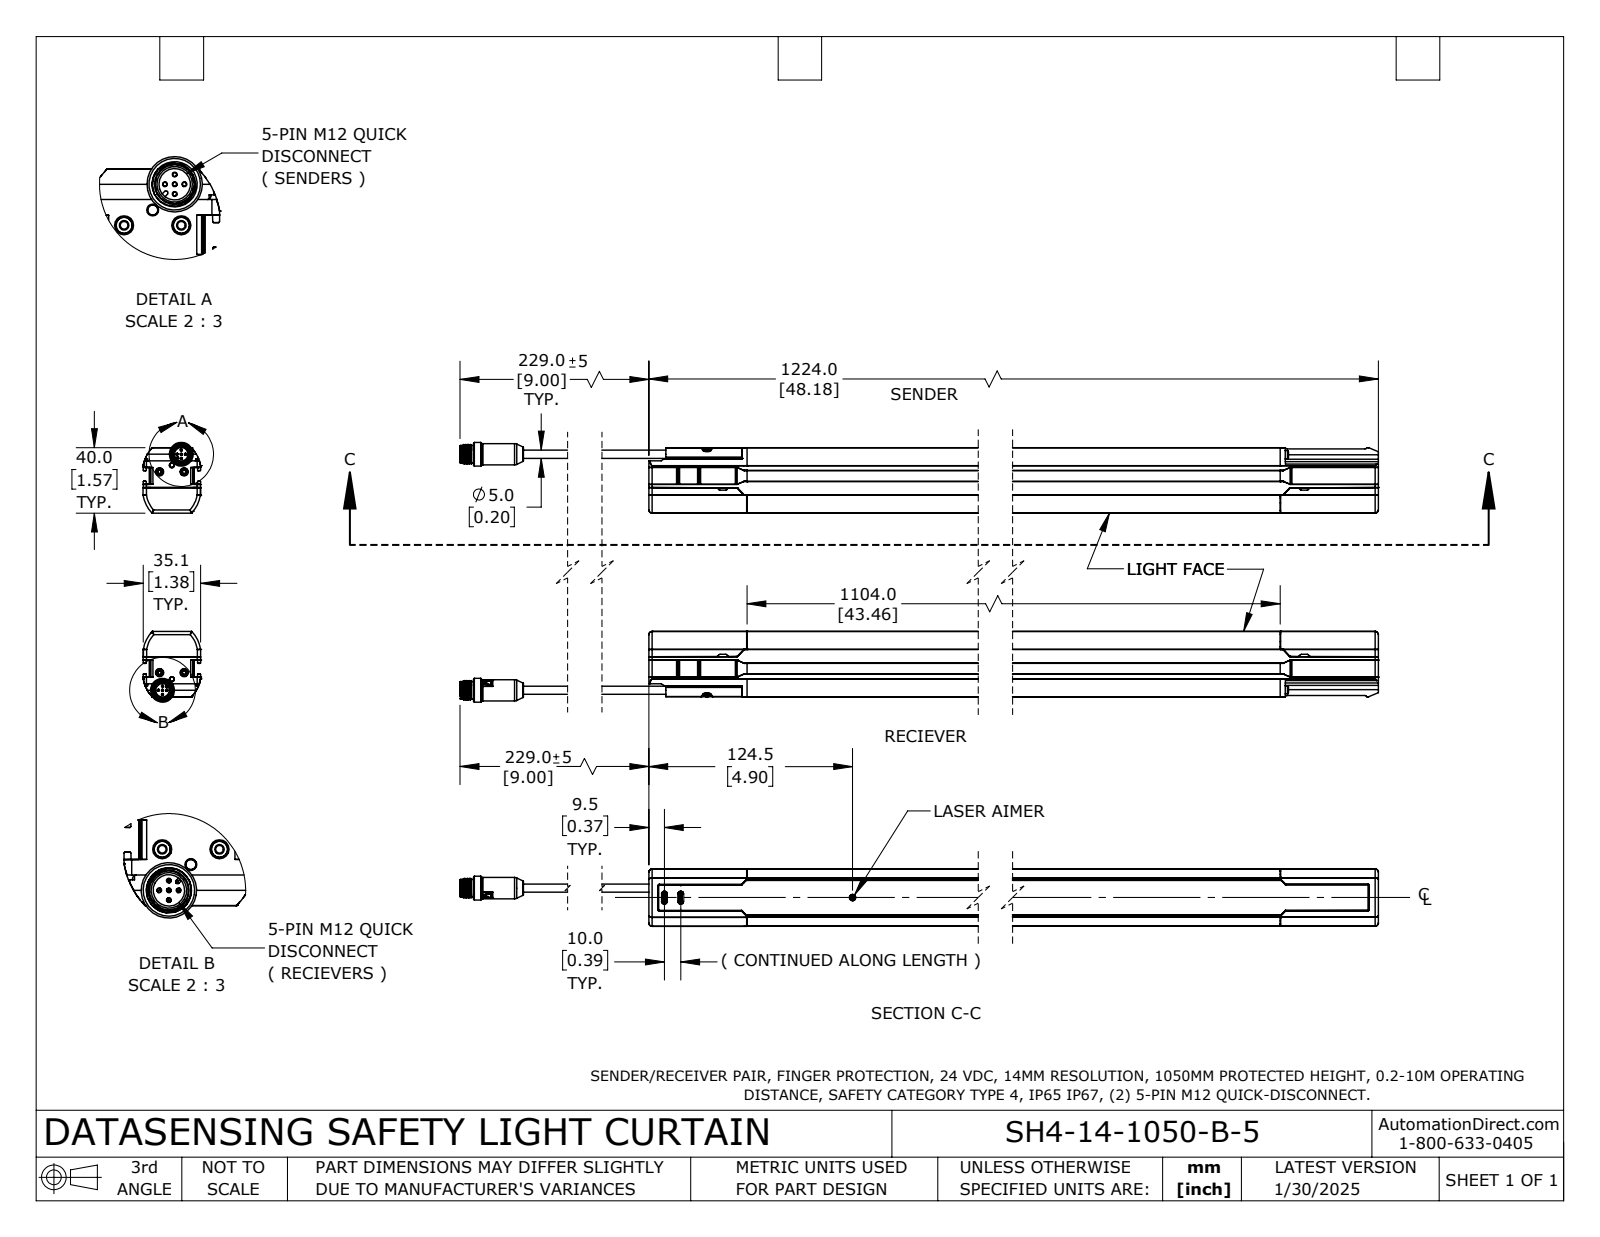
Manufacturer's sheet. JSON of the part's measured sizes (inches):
{"part_name": "957920006", "step_written_by": "SolidWorks 2024 (AUTOMOTIVE_DESIGN)", "units": "inches", "bodies": {"solids": 4, "faces": 2574, "planar": 1170, "cylindrical": 778, "other": 626}, "overall_size": [50.681, 6.248, 1.384], "volume_in3": 152.2, "surface_area_in2": 673.2, "round_holes": [[0.079, 4], [0.118, 4], [0.197, 4], [0.1, 2], [0.101, 2], [0.102, 2], [0.102, 2], [0.11, 2], [0.325, 2], [0.382, 2], [0.407, 2], [0.425, 2]], "round_bosses_or_shafts": [[0.197, 10], [0.039, 10], [0.087, 8], [0.172, 4], [0.571, 2], [0.512, 2], [0.417, 2], [0.374, 2]], "partial_cylinders_radius": [[0.01, 164], [0.016, 66], [0.02, 50], [0.008, 36], [0.031, 20], [0.031, 12], [0.079, 12], [0.059, 10]], "face_to_face_distances": [1.496, 4.496, 0.156, 1.222, 3, 1.378, 5.992, 1.067, 4.634, 1.033], "hole_center_spacings": [0.866, 5.322, 5.392, 0.429, 0.591, 0.672, 4.831, 4.867]}
